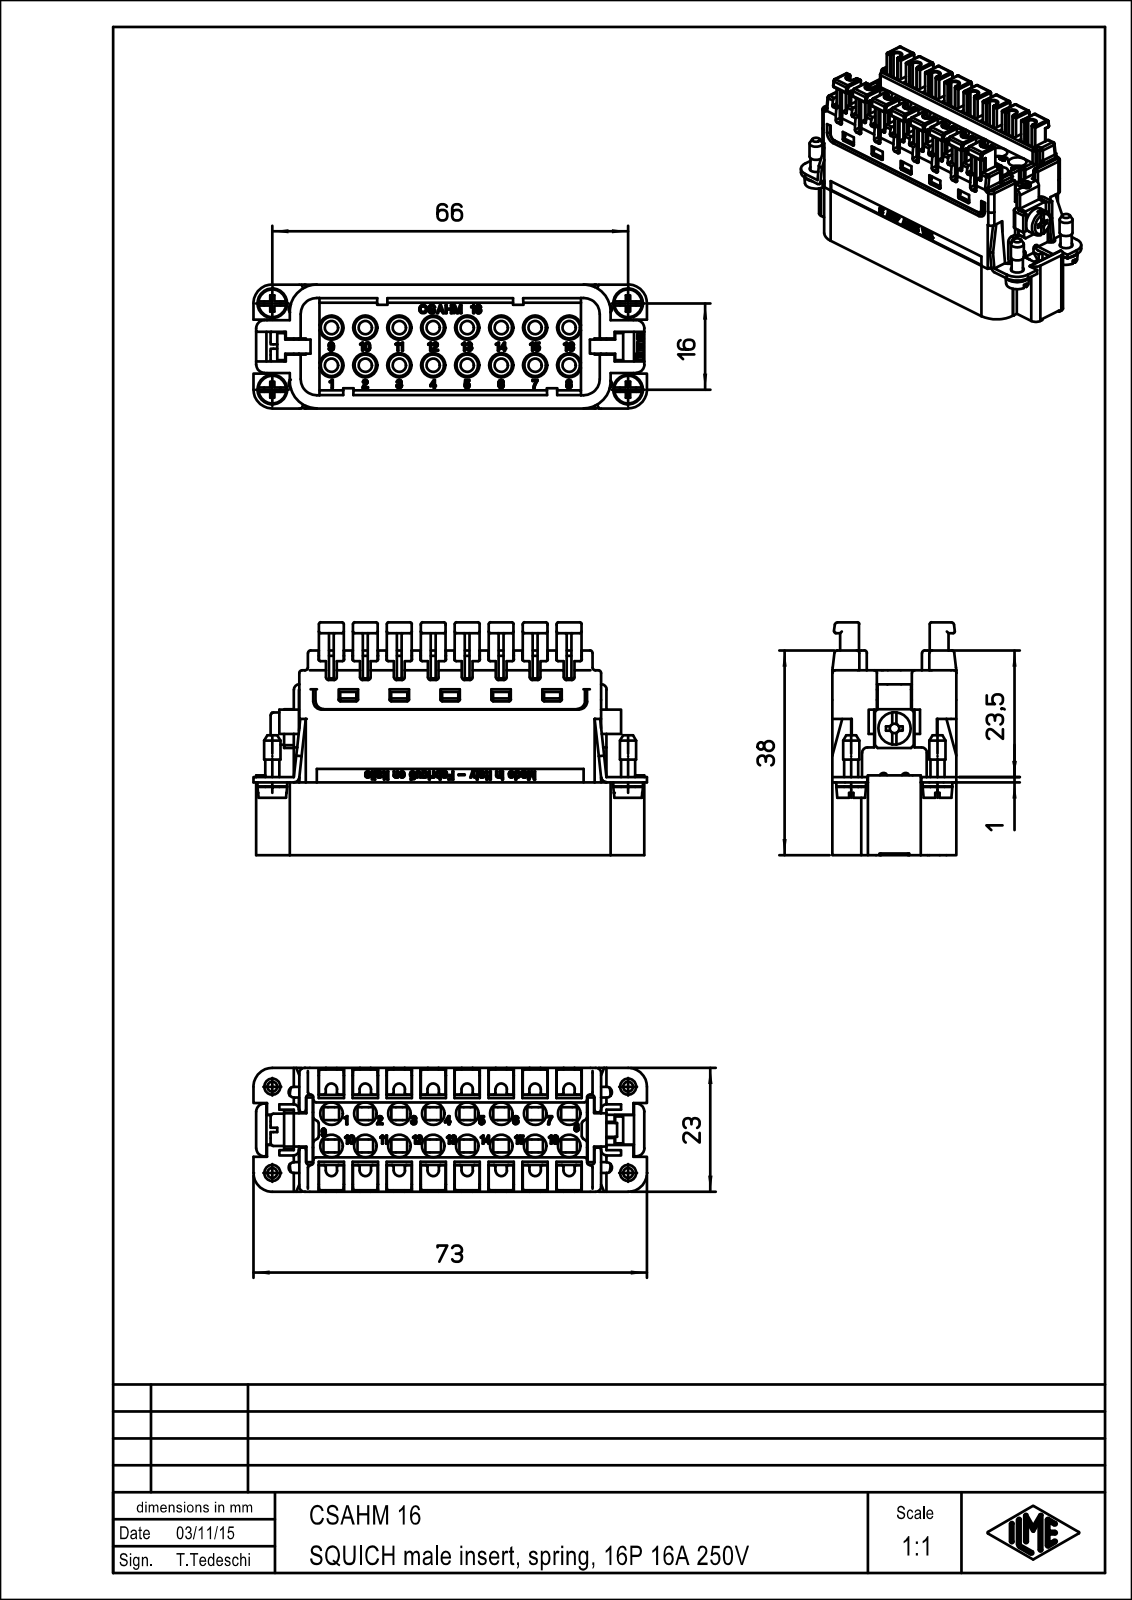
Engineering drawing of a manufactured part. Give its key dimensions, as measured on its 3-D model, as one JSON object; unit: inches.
{"part_name": "CSAHM_16", "step_written_by": "PTC Creo Elements/Direct Modeling 19.0B 21-Mar-2015 (C) Parametric Technology GmbH (AUTOMOTIVE_DESIGN)", "units": "inches", "bodies": {"solids": 1, "faces": 2044, "planar": 1368, "cylindrical": 440, "other": 236}, "overall_size": [2.874, 1.701, 0.906], "volume_in3": 2.085, "surface_area_in2": 36.84, "round_holes": [[0.165, 16], [0.138, 1]], "round_bosses_or_shafts": [[0.098, 16], [0.217, 4], [0.118, 4], [0.236, 1]], "partial_cylinders_radius": [[0.008, 64], [0.02, 58], [0.039, 20], [0.041, 16], [0.059, 8], [0.016, 4], [0.079, 4], [0.118, 4]], "face_to_face_distances": [0.906, 0.654, 0.248, 0.057, 0.039, 0.138, 0.197, 0.14, 0.195, 0.496], "hole_center_spacings": [0.248, 0.343, 0.496, 0.55, 0.744, 0.781, 0.236, 0.992]}
